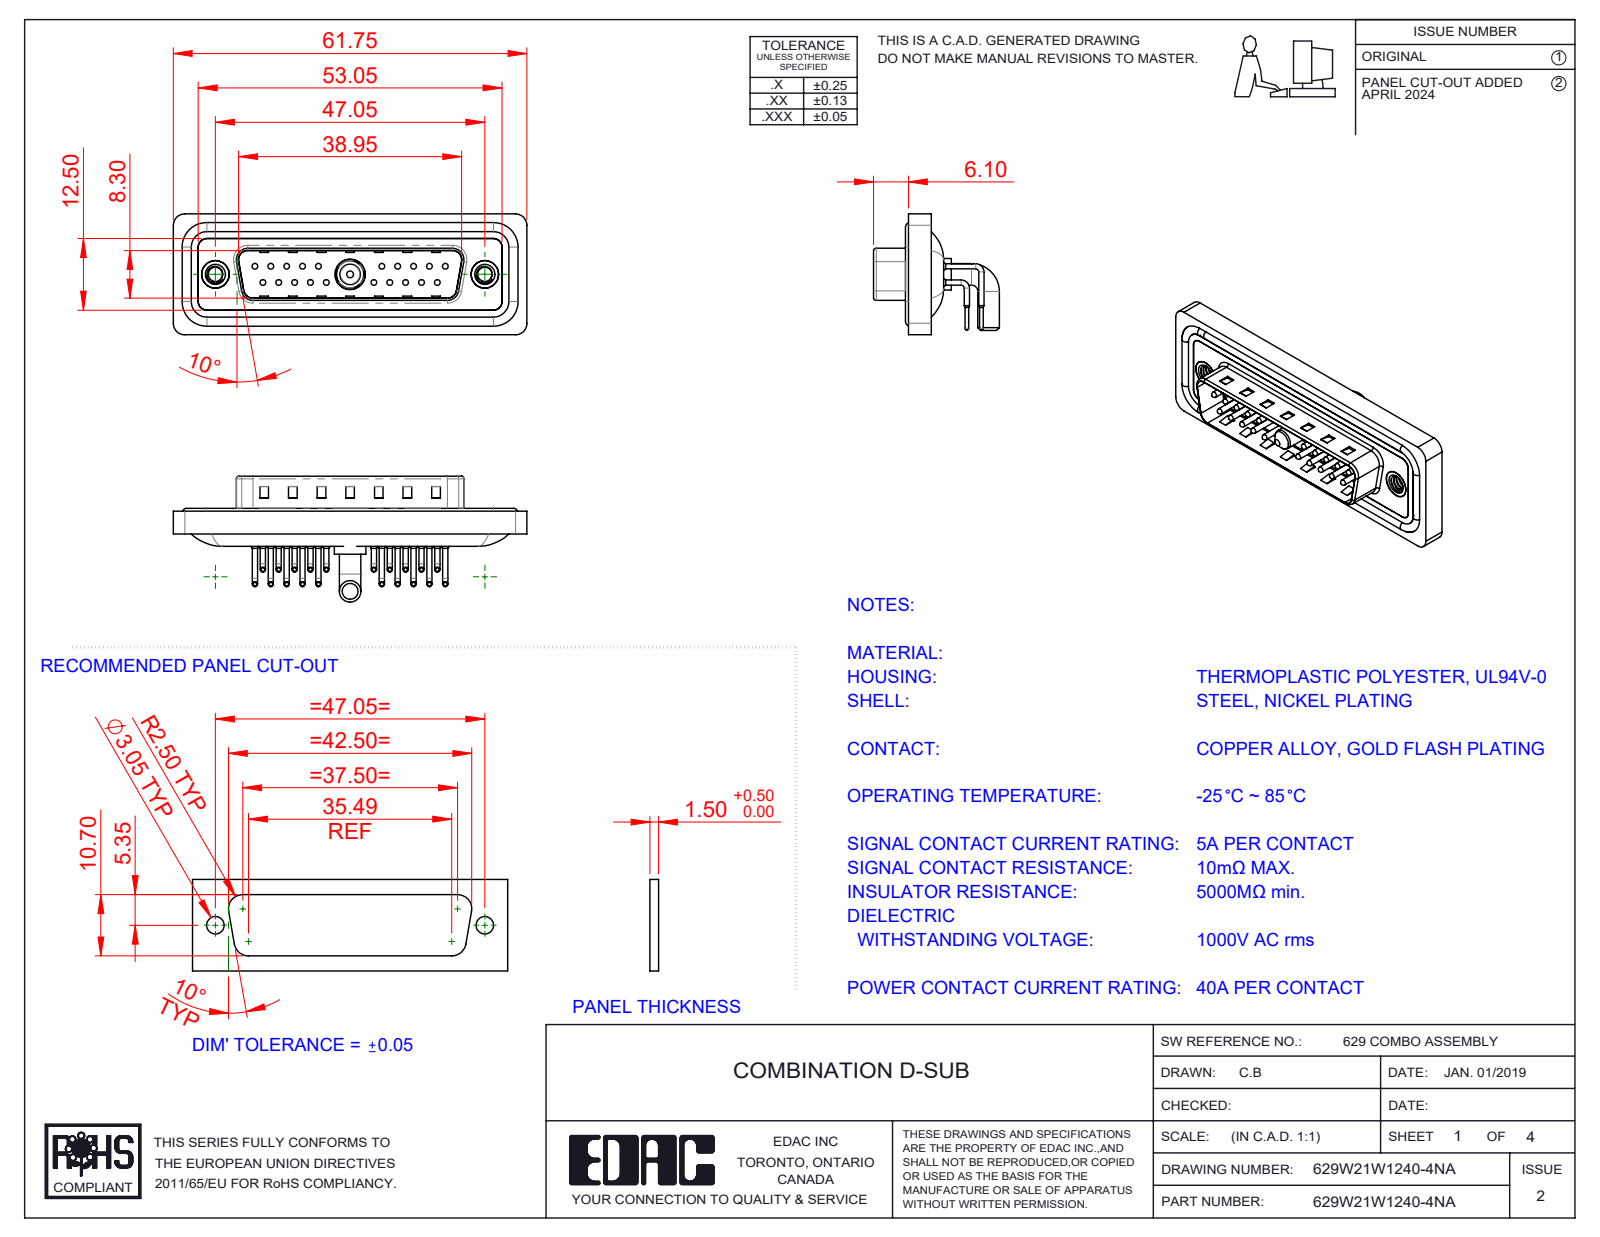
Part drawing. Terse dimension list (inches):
name: 629Combo Shell Front_25 Contacts; 629Combo Contact Row 1; 629Combo Waterproof Housing_25 Contacts; 629Combo Contact Row 2 (+5 more)
written by: SolidWorks 2023 (CONFIG_CONTROL_DESIGN)
unit: in
bodies: 29 solids, 2720 faces (1499 planar, 927 cylindrical, 294 other)
size: 2.431 × 0.865 × 0.831
volume: 0.457 in³; area: 19.79 in²
holes: 20× ⌀0.03, 20× ⌀0.063, 20× ⌀0.079, 2× ⌀0.098, 2× ⌀0.157, 2× ⌀0.189, 2× ⌀0.197, 1× ⌀0.191, 1× ⌀0.209
bosses: 40× ⌀0.035, 20× ⌀0.059, 20× ⌀0.039, 20× ⌀0.026, 4× ⌀0.063, 2× ⌀0.193, 2× ⌀0.148, 1× ⌀0.217
rounds: 20× R0.04, 18× R0.059, 18× R0.079, 8× R0.02, 8× R0.063, 4× R0.01, 4× R0.024, 4× R0.026
face distances: 0.016, 0.114, 0.031, 0.161, 0.043, 0.083, 0.063, 0.177, 0.059, 0.098
hole spacings: 0.124, 0.109, 0.218, 0.327, 0.198, 0.763, 0.826, 0.872
